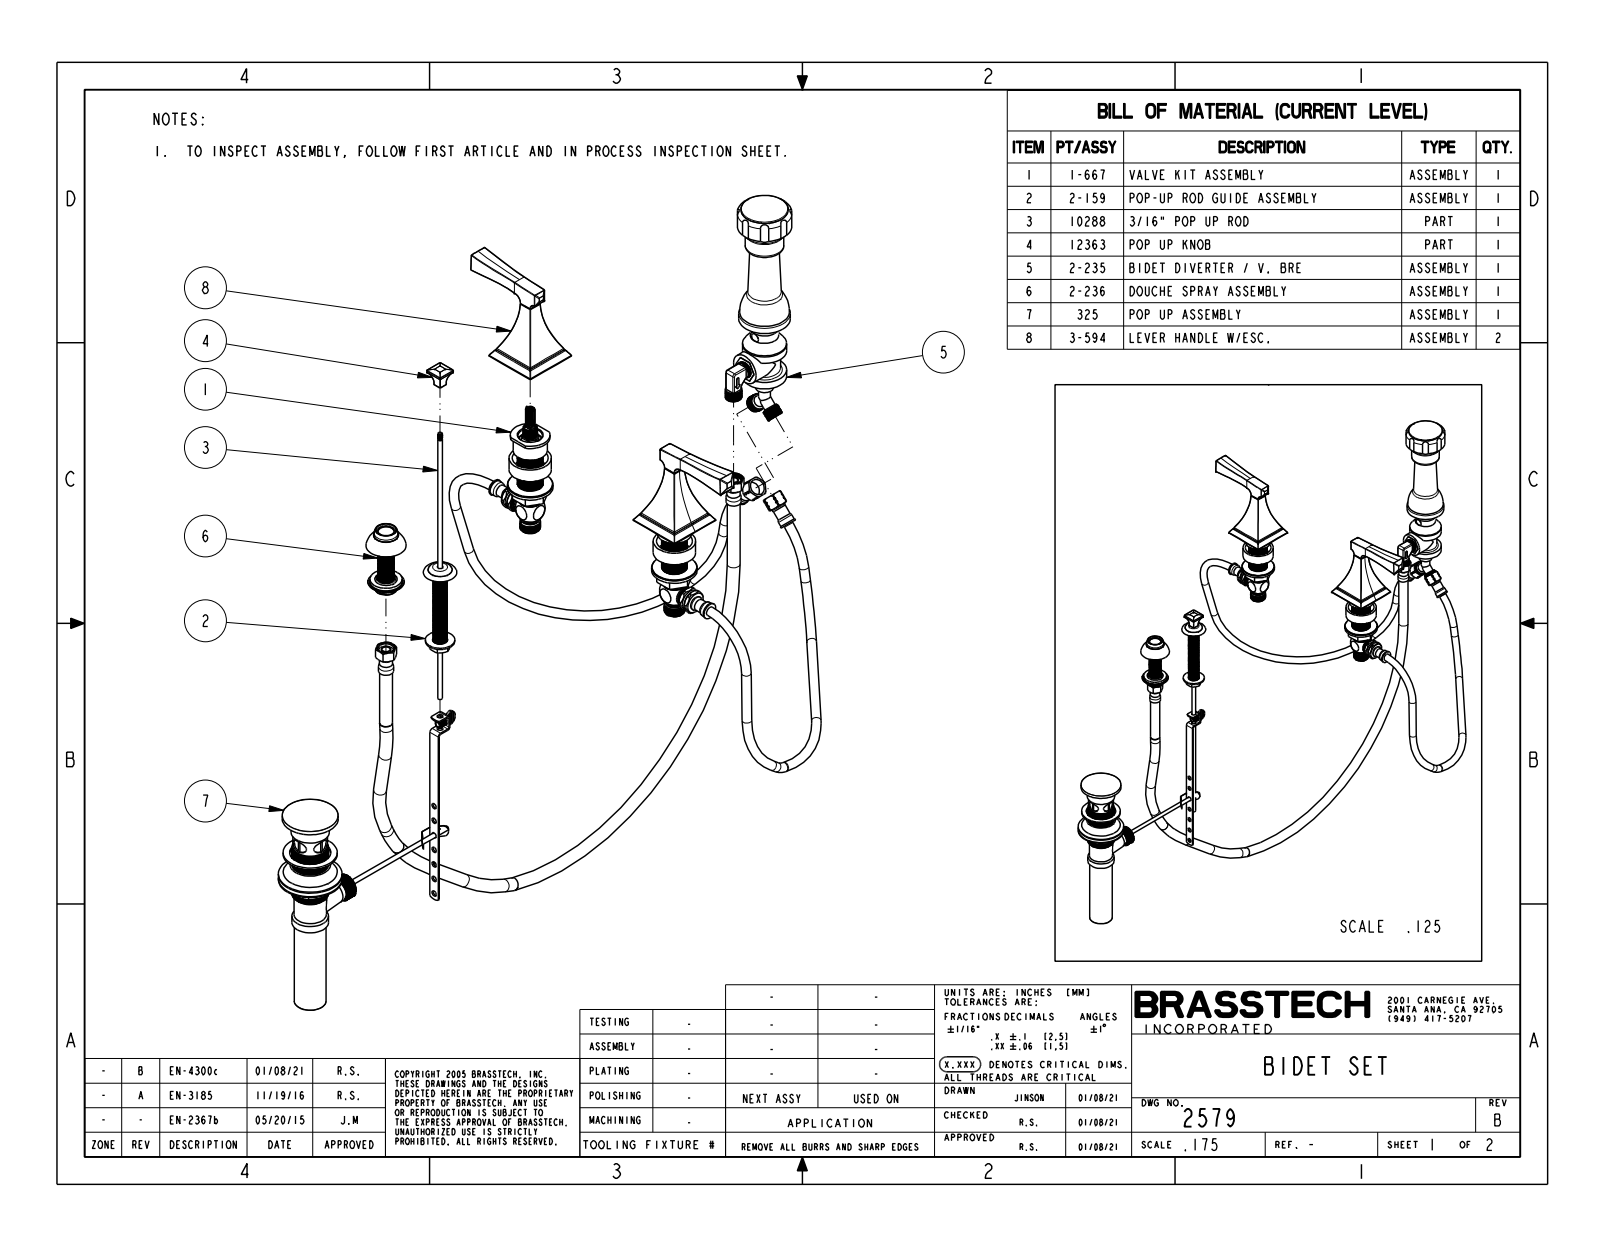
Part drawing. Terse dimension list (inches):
name: 2579
written by: CREO PARAMETRIC BY PTC INC, 2018400 (CONFIG_CONTROL_DESIGN)
unit: in
bodies: 5 solids, 492 faces (76 planar, 114 cylindrical, 302 other)
size: 22.855 × 14.104 × 5.353
volume: 23.15 in³; area: 103.8 in²
holes: 1× ⌀0.625, 1× ⌀0.792, 1× ⌀0.94
bosses: 2× ⌀0.506, 1× ⌀2.025, 1× ⌀1.52, 1× ⌀0.925, 1× ⌀0.775
rounds: 52× R0.02, 16× R0.06, 8× R0.21, 4× R0.04, 1× R0.357, 1× R1.077
face distances: 0.56, 3.468, 0.674, 2.794, 2.5, 1.826, 0.969, 2.531, 1.857, 0.031
